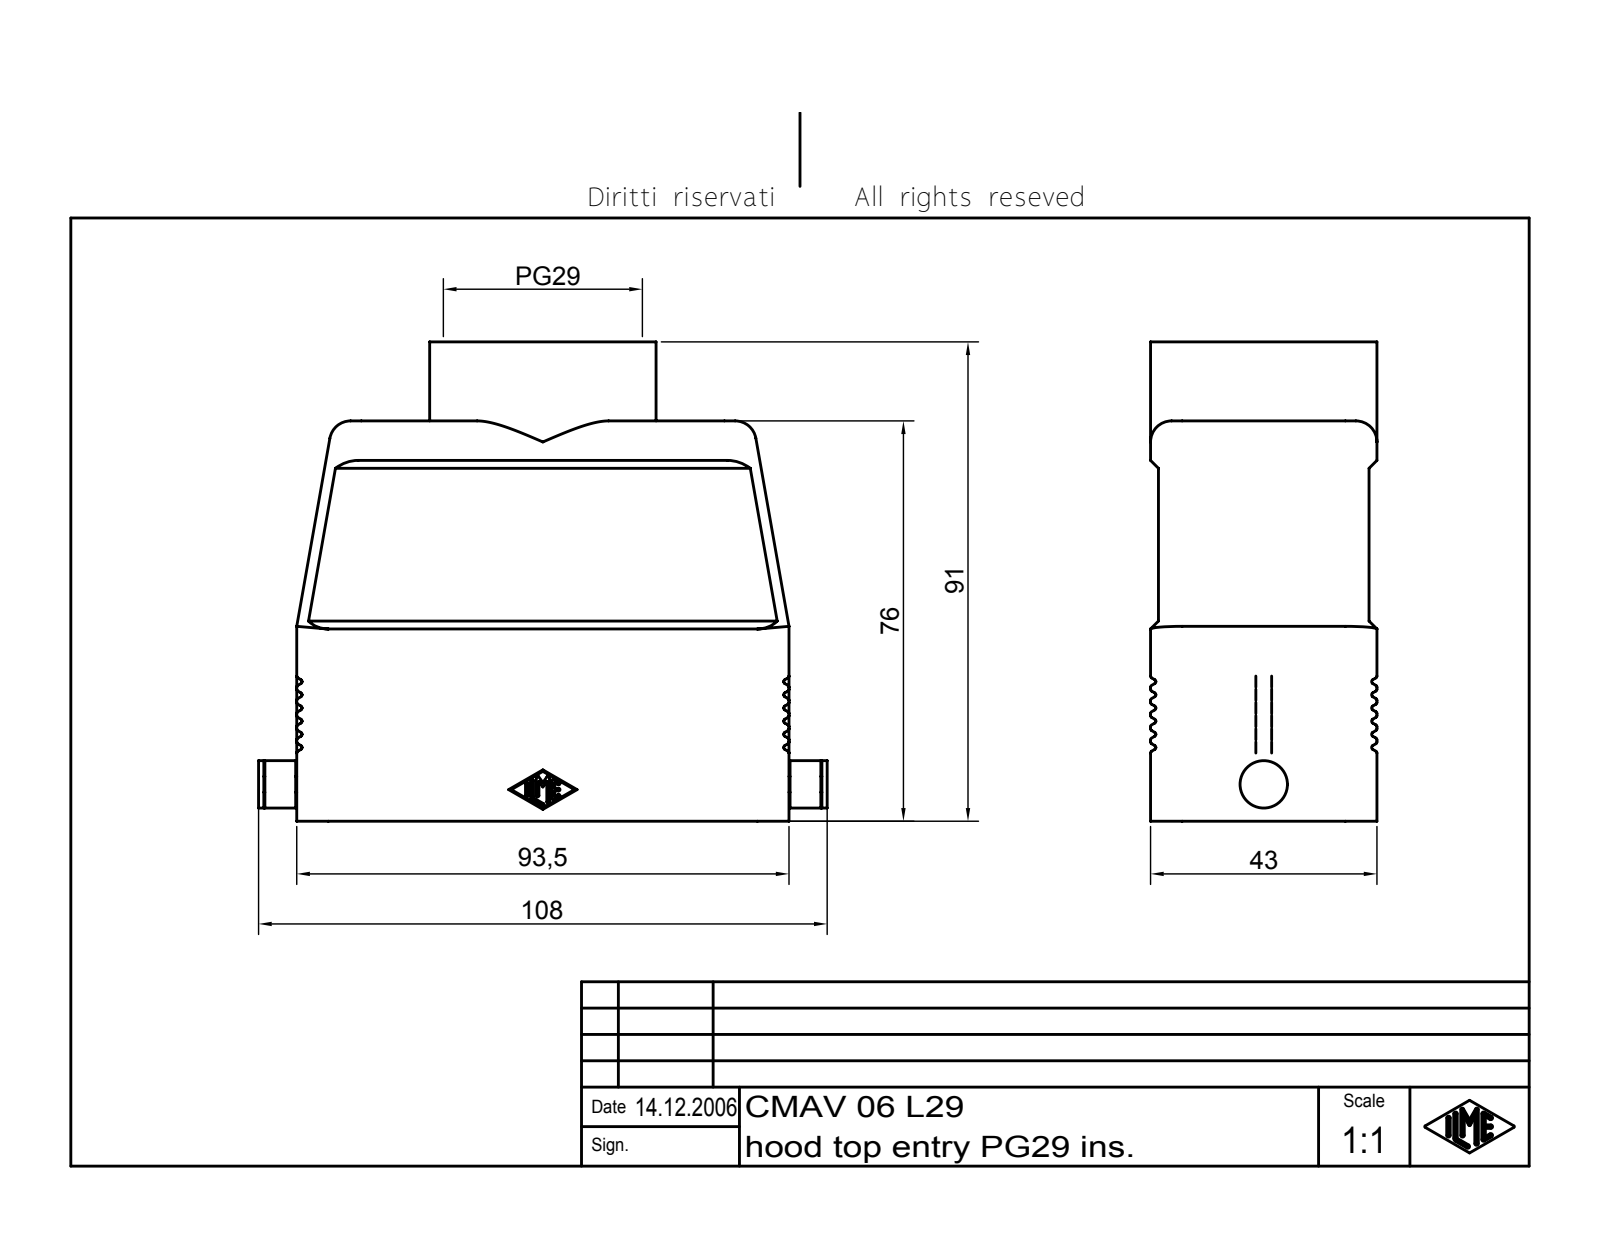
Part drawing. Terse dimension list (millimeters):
name: CMAV 06 L29
written by: Autodesk Inventor 7 (AUTOMOTIVE_DESIGN)
unit: mm
bodies: 1 solid, 843 faces (150 planar, 420 cylindrical, 273 other)
size: 108 × 91 × 43
volume: 73 213 mm³; area: 48 873 mm²
holes: 1× ⌀33.7, 1× ⌀35.48
bosses: 1× ⌀43, 1× ⌀9, 1× ⌀3
rounds: 96× R0.4, 14× R0.25, 8× R6, 4× R1.5, 4× R3, 4× R4, 2× R5
face distances: 1.5, 3, 40, 37, 38.5, 41.5, 43, 90.5, 8.25, 79.25
